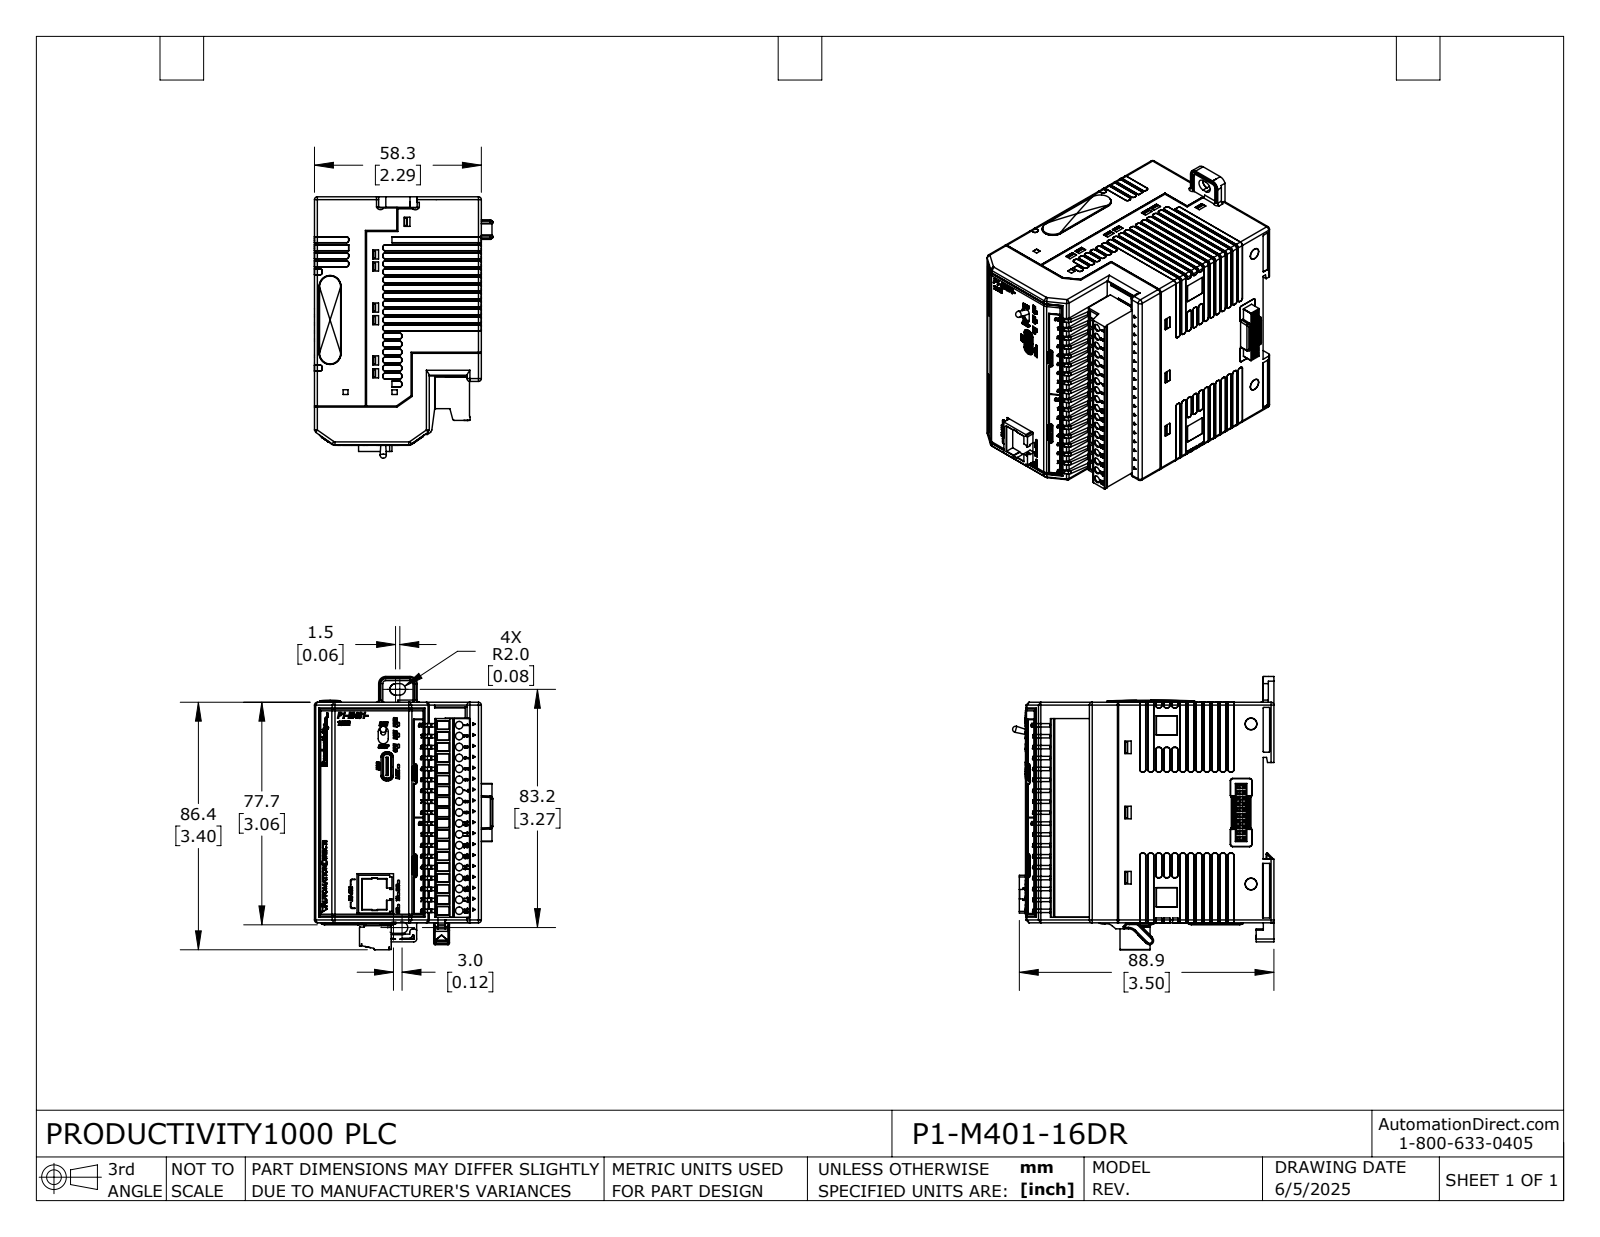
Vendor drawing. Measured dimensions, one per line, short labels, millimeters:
name: P1-M401-16DR
written by: SolidWorks 2024 (AUTOMOTIVE_DESIGN)
unit: mm
bodies: 20 solids, 3471 faces (1930 planar, 871 cylindrical, 670 other)
size: 93.6 × 91.3 × 62.3
volume: 33 970 mm³; area: 66 450 mm²
rounds: 172× R0.3, 78× R0.2, 53× R0.5, 33× R1, 10× R0.1, 8× R2, 7× R0.6, 4× R0.3
face distances: 56.8, 0.5, 1, 57.8, 76.5, 76.8, 58.3, 58.3, 57.3, 76.7
